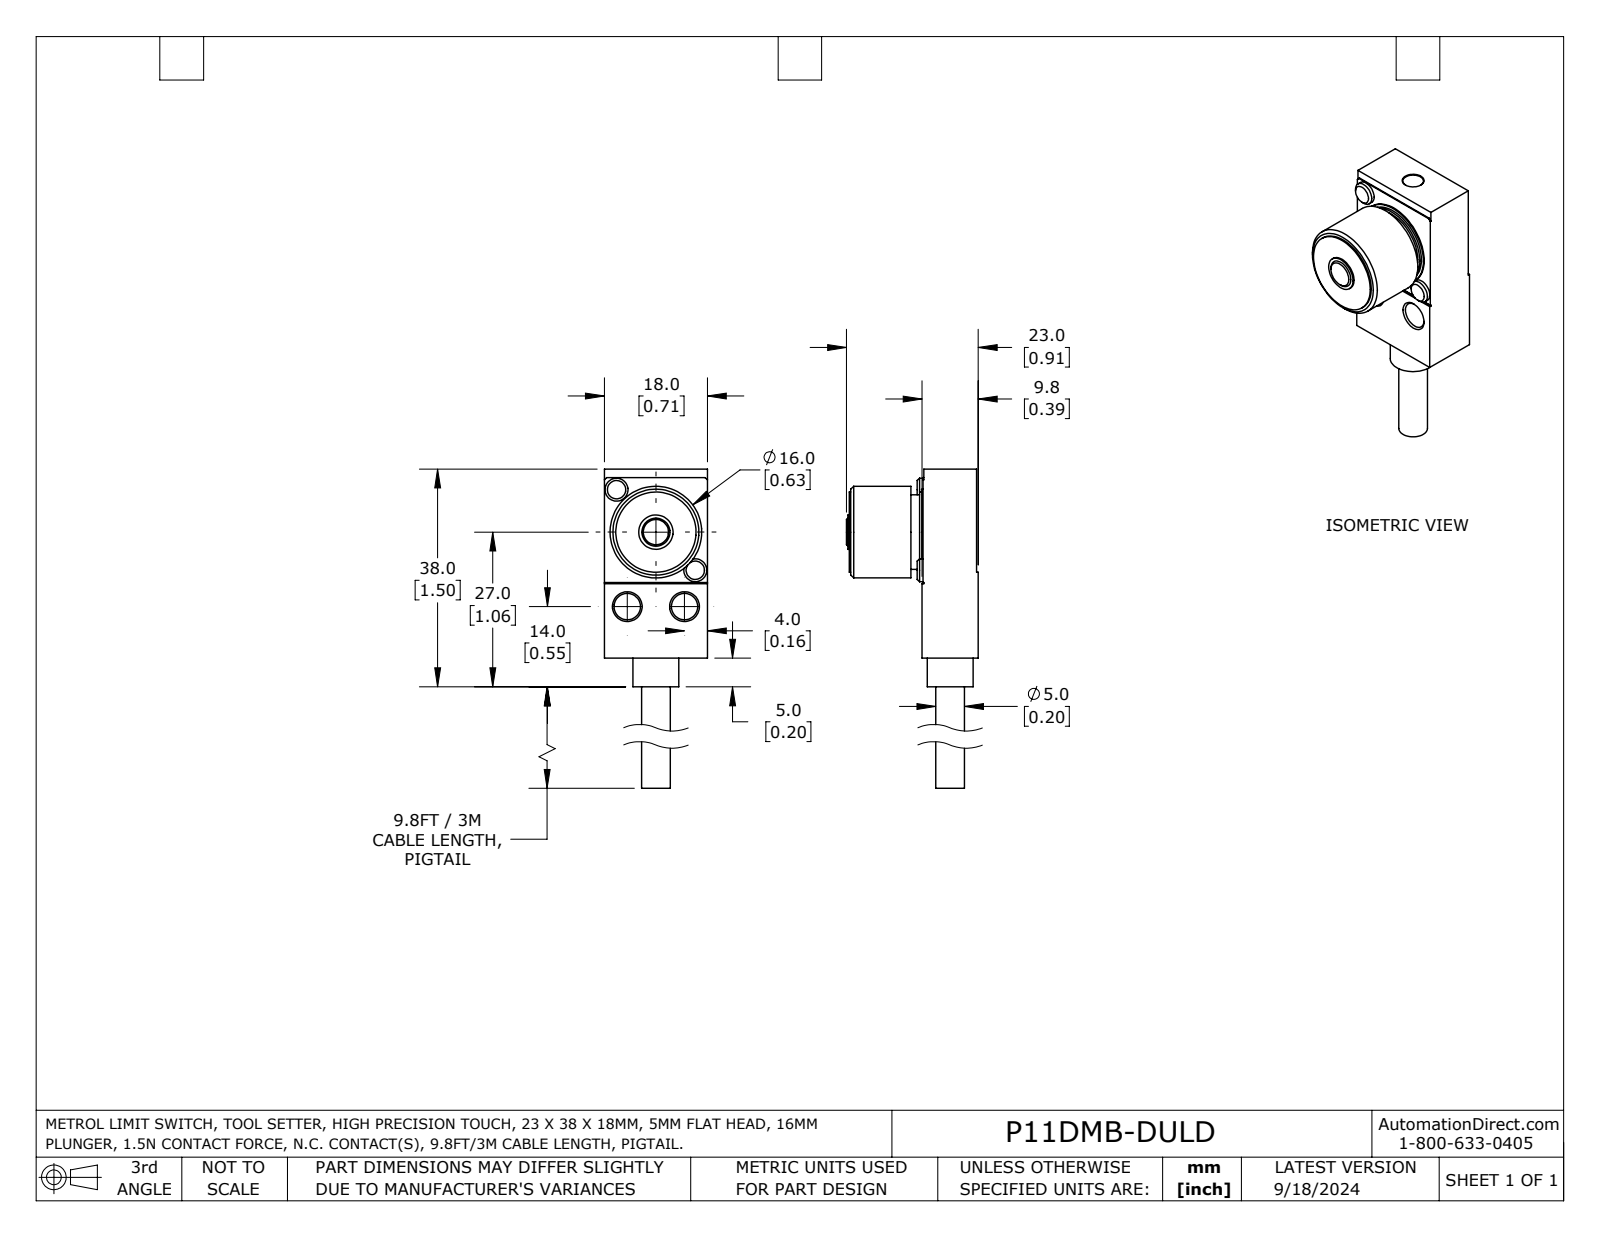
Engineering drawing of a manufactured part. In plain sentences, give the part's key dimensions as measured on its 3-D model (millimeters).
The part is named "P11DDB-DULD". Its 3-D file was written by "SolidWorks 2023 (AUTOMOTIVE_DESIGN)". It is 1 solid with 47 faces: 28 planar, 12 cylindrical and 7 other. Overall it measures 53 by 23 by 18 millimeters. Its volume is 8 357 cubic millimeters and its surface area 3 523 square millimeters. Round holes: 2 of diameter 4.6. Round bosses or shafts: 2 of diameter 4, 1 of diameter 16, 1 of diameter 15, 1 of diameter 14, 1 of diameter 13, 1 of diameter 8, 1 of diameter 6, 1 of diameter 5. The main face-to-face distances are 18, 9.5, 9.8, 33, 9.65, 9.35, 22.5, 22.2, 12.85, 12.7. The hole center spacings are 10.
